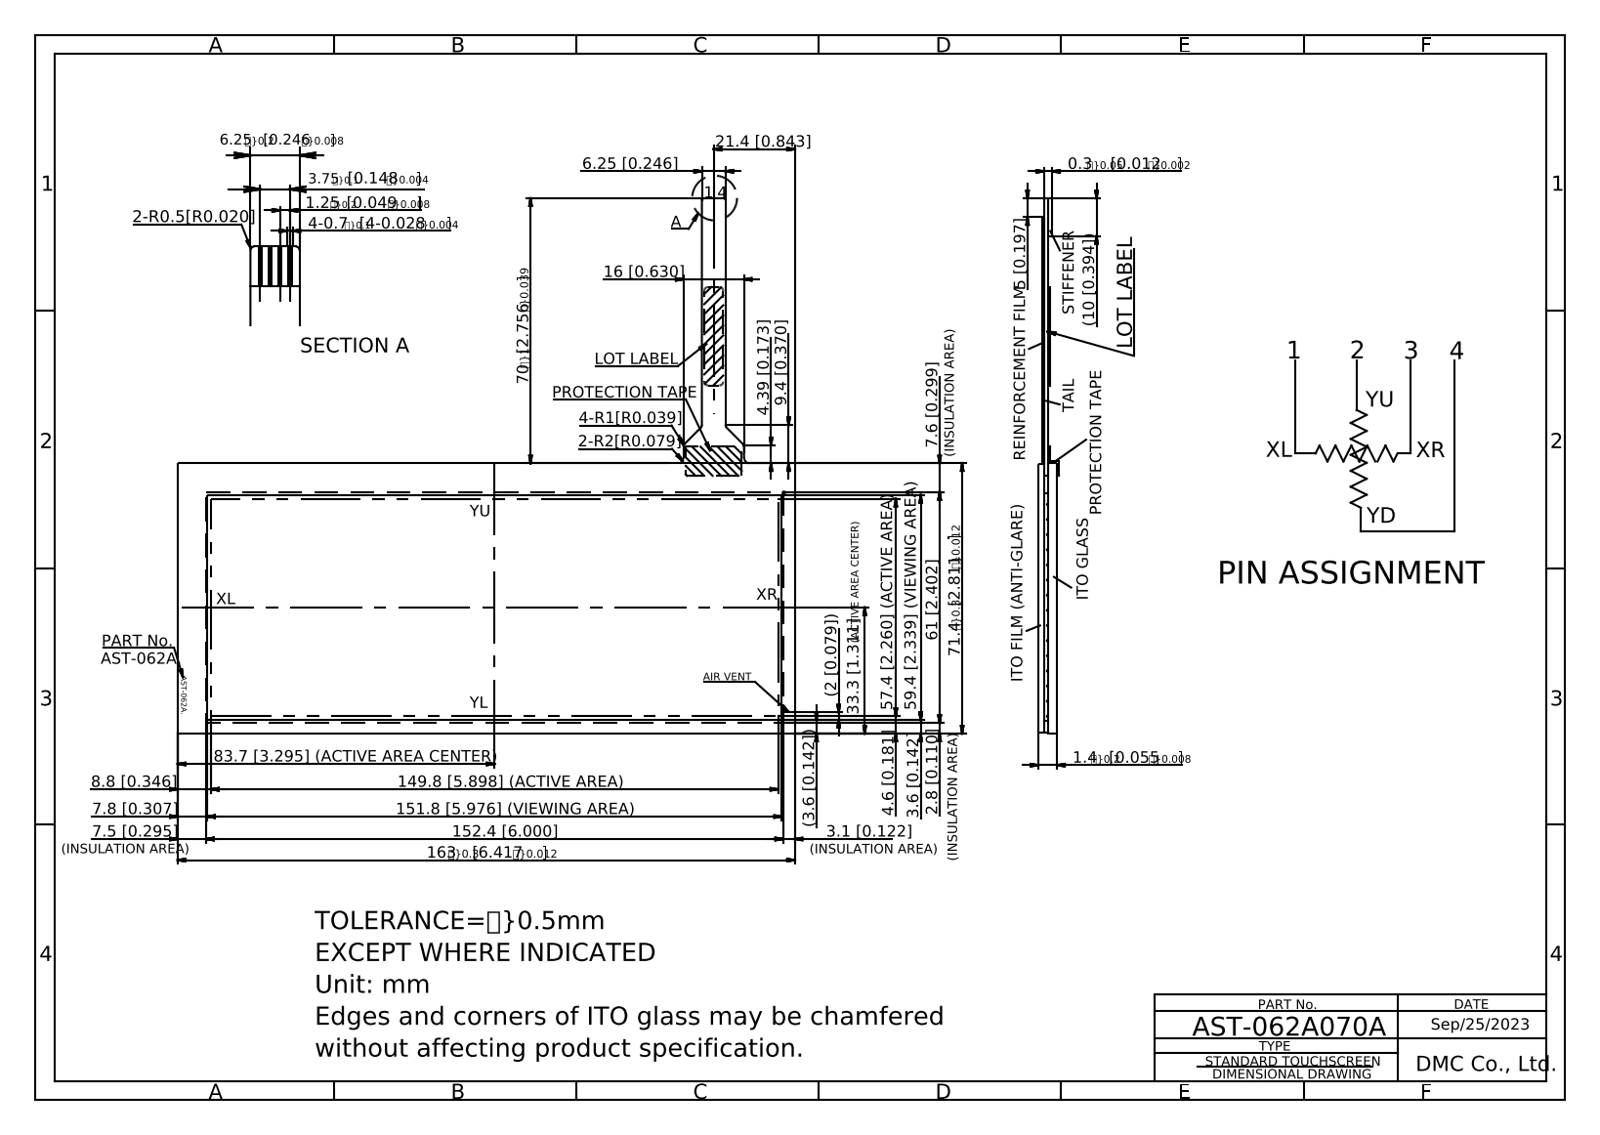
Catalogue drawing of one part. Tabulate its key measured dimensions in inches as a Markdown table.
| quantity | value |
| --- | --- |
| part name | AST-062A070A |
| STEP written by | Autodesk Inventor 2020 (CONFIG_CONTROL_DESIGN) |
| units | inches |
| bodies | 1 solid, 51 faces (45 planar, 6 cylindrical, 0 other) |
| overall size | 8.984 × 6.129 × 0.055 |
| volume | 0.996 in³ |
| surface area | 38.83 in² |
| partial cylindrical surfaces (radius × count) | 0.039 × 4, 0.02 × 2 |
| main face-to-face distances | 0.055, 0.047, 0.043, 0.051, 2.811, 6.417, 0.031, 0.016, 0.02, 0.024 |
